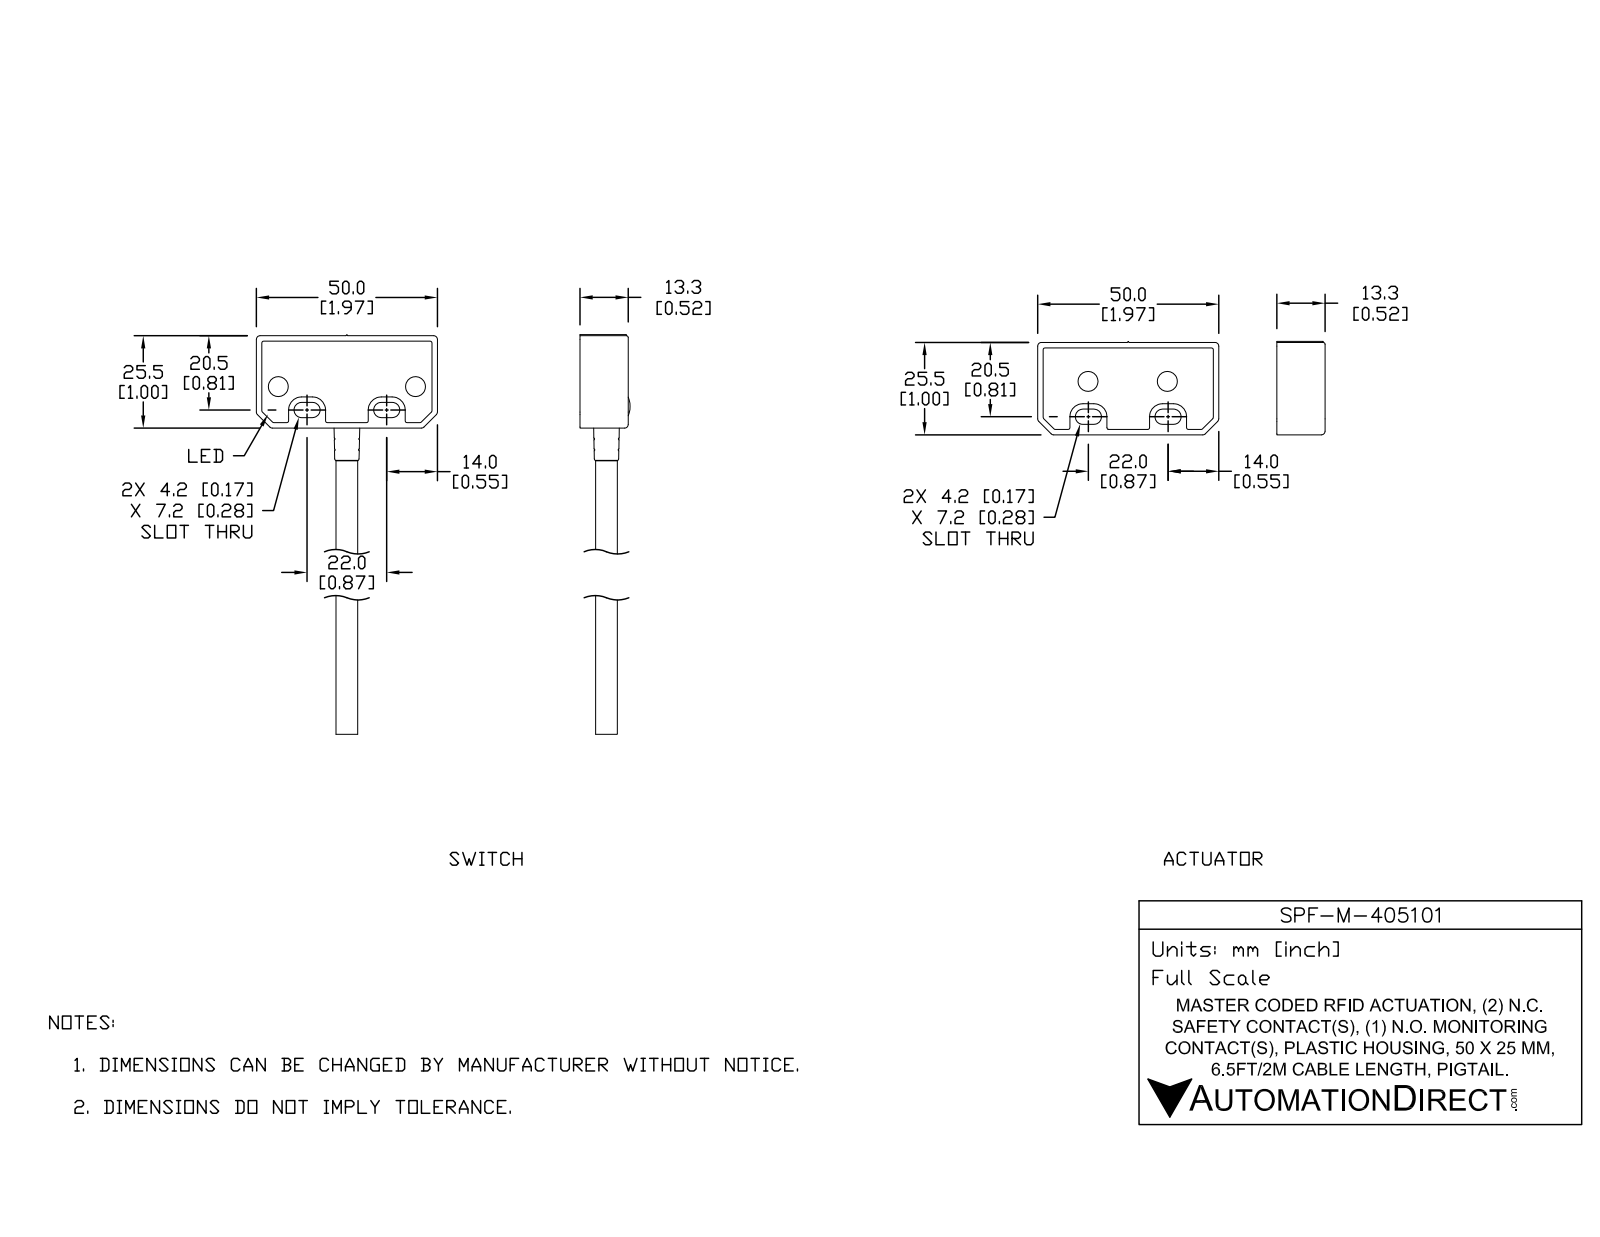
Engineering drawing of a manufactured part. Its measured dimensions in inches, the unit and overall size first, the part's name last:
Units: inches
Overall size (bounding box): 8.091 × 1.969 × 0.543
Round holes (diameter × count): ⌀0.197 ×4, ⌀0.119 ×1, ⌀0.173 ×1, ⌀0.213 ×1, ⌀0.232 ×1, ⌀0.276 ×1
Round bosses / shafts (diameter × count): ⌀0.079 ×4, ⌀0.193 ×2, ⌀0.031 ×2, ⌀0.339 ×1, ⌀0.299 ×1, ⌀0.28 ×1, ⌀0.236 ×1, ⌀0.209 ×1
Partial cylindrical surfaces — rounded edges, fillets, slot ends (radius × count): R0.02 ×132, R0.039 ×36, R0.079 ×8, R0.083 ×8, R0.142 ×8, R0.181 ×8, R0.012 ×6, R0.14 ×4
Main face-to-face distances: 0.059, 0.457, 0.398, 0.047, 0.445, 0.504, 1.043, 0.098, 0.945, 1.909
Hole centre spacings: 0.221, 0.862, 1.062, 1.065, 1.283, 1.492, 1.55, 1.559
Volume: 1.105 in³ · Surface area: 36.31 in²
Bodies: 12 solids, 1147 faces (475 planar, 358 cylindrical, 314 other)
Part name (STEP PRODUCT): SPF-M-405101; SPF-M-405101_2; SPF-M-405101_1
STEP written by: SolidWorks 2017 (AUTOMOTIVE_DESIGN)
